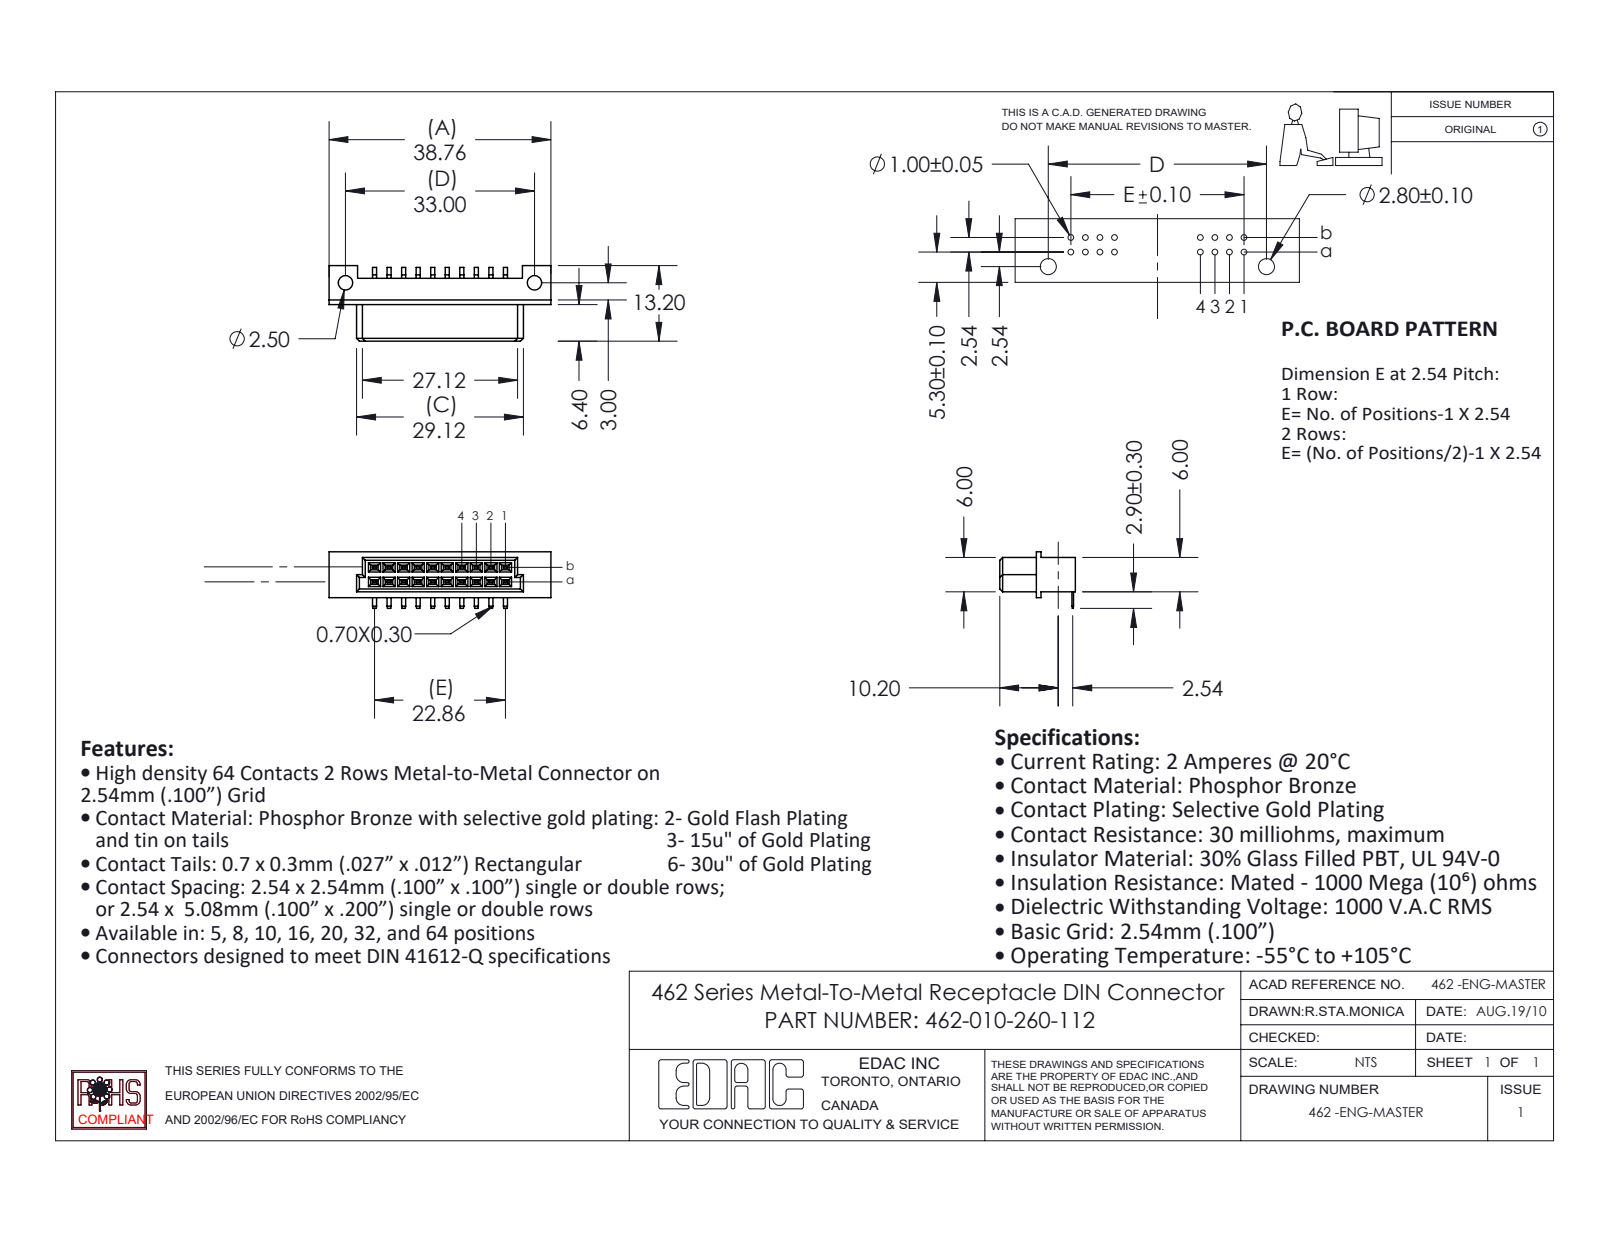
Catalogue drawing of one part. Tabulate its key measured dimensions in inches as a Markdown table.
| quantity | value |
| --- | --- |
| part name | 462 Part_20; 462-010-260-112; 462-290-1 |
| STEP written by | SolidWorks 2020 (CONFIG_CONTROL_DESIGN) |
| units | inches |
| bodies | 11 solids, 435 faces (411 planar, 24 cylindrical, 0 other) |
| overall size | 1.526 × 0.52 × 0.39 |
| volume | 0.13 in³ |
| surface area | 3.906 in² |
| round holes (diameter × count) | 0.098 × 2 |
| partial cylindrical surfaces (radius × count) | 0.04 × 1, 0.052 × 1 |
| main face-to-face distances | 0.236, 0.1, 0.181, 0.032, 0.039, 0.062, 0.074, 0.162, 0.174, 0.022 |
| hole center spacings | 1.299 |
